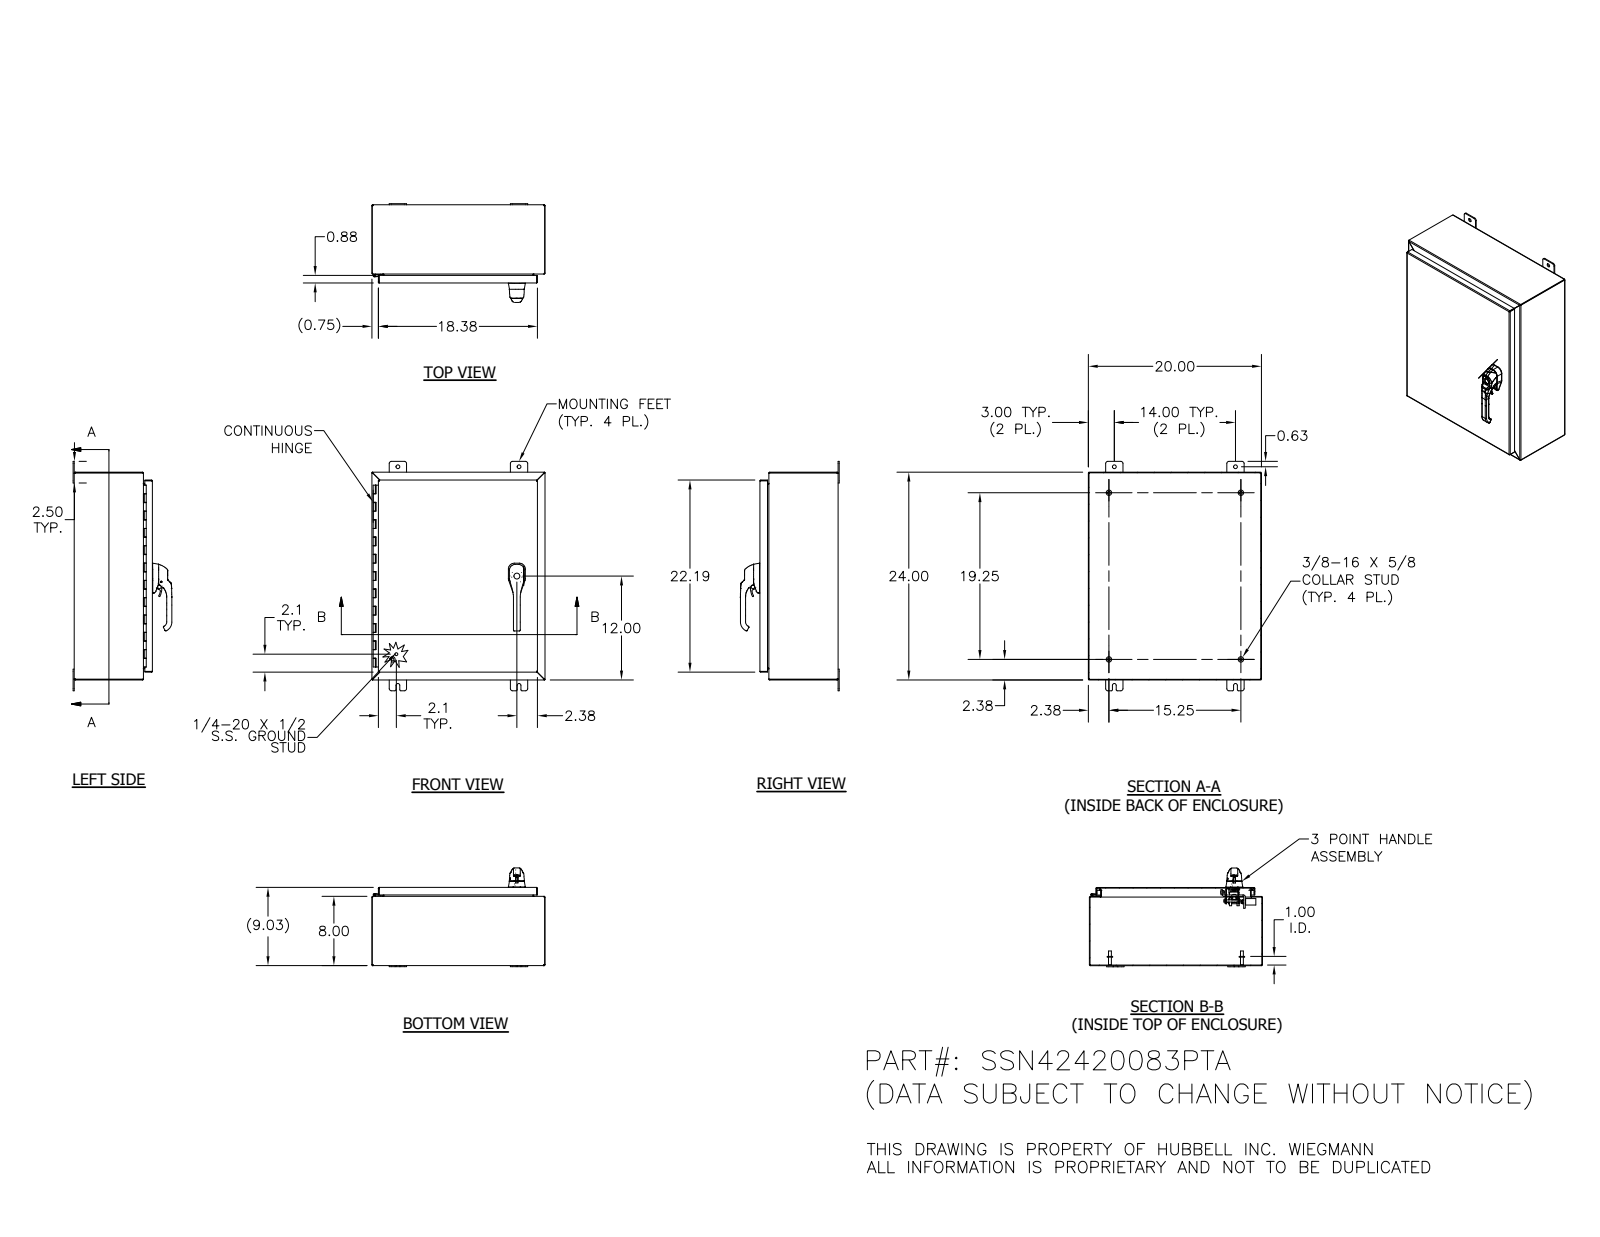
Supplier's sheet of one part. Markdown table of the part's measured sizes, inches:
| quantity | value |
| --- | --- |
| part name | SSN42420083PT; 34871; SSN42420083PTBKP; HFW32451 (+8 more) |
| STEP written by | Autodesk Inventor 2012 (AUTOMOTIVE_DESIGN) |
| units | inches |
| bodies | 56 solids, 2624 faces (1022 planar, 961 cylindrical, 641 other) |
| overall size | 26.5 × 20 × 11.408 |
| volume | 163.2 in³ |
| surface area | 4 173 in² |
| round holes (diameter × count) | 0.262 × 8, 0.187 × 4, 0.438 × 4, 0.213 × 3, 0.281 × 3, 0.241 × 2, 0.25 × 2, 0.252 × 2, 0.315 × 2, 0.4 × 2, 0.402 × 2, 0.413 × 2 |
| round bosses / shafts (diameter × count) | 0.625 × 4, 0.33 × 4, 0.236 × 3, 1 × 2, 0.563 × 2, 0.533 × 2, 0.531 × 2, 0.5 × 2 |
| partial cylindrical surfaces (radius × count) | 0.02 × 172, 0.012 × 113, 0.125 × 26, 0.031 × 24, 0.019 × 21, 0.105 × 20, 0.25 × 20, 0.025 × 16 |
| main face-to-face distances | 0.074, 8.959, 8.885, 9.033, 19.926, 23.926, 7.926, 1.033, 19.852, 20 |
| hole center spacings | 0.38, 0.492, 0.76, 0.886, 14.428, 0.234, 0.258, 0.38 |
